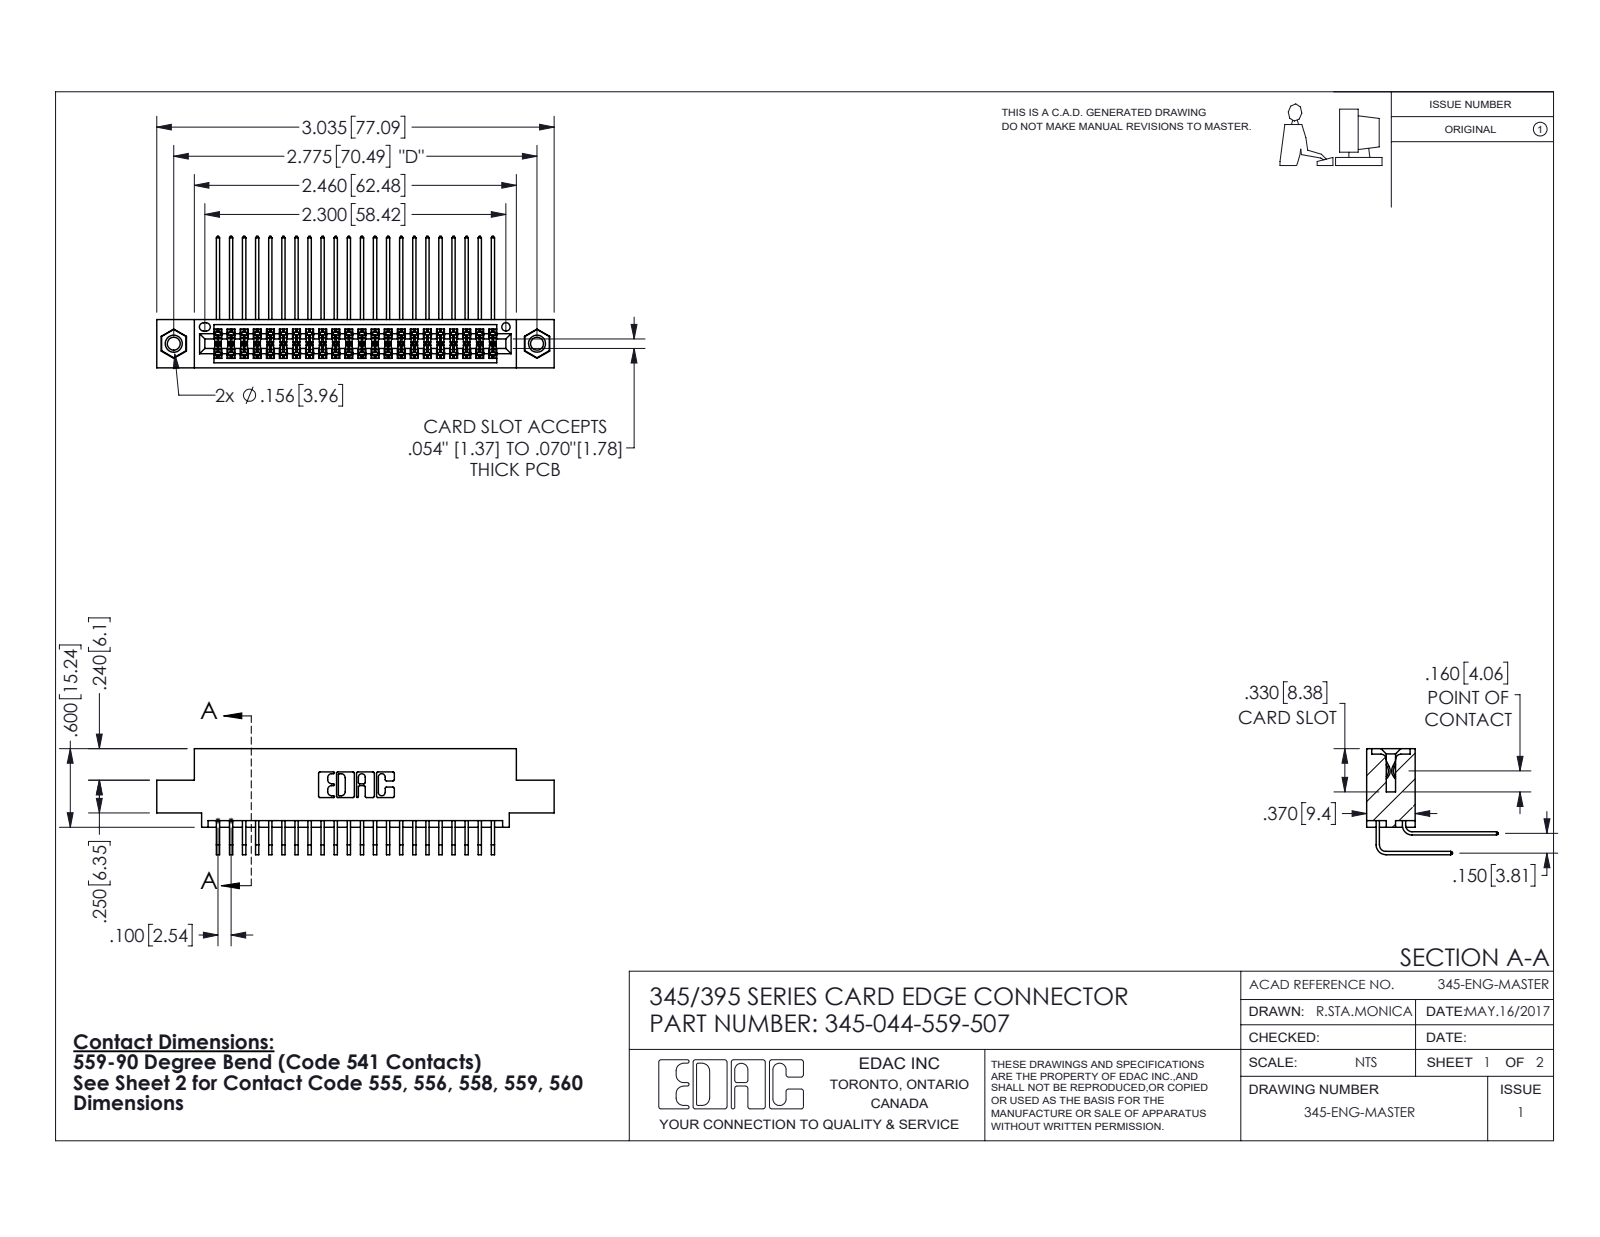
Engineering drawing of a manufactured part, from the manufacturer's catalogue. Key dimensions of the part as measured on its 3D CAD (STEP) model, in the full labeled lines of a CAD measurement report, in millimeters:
Part name (STEP PRODUCT): 345-292-001_559 Tail - 2; 345-044-559-507; 345-250-001_345-250-005-103; 345-292-001_558 559 Tail - 1 (+1 more)
STEP written by: SolidWorks 2016 (CONFIG_CONTROL_DESIGN)
Units: millimetres
Bodies: 47 solids, 2478 faces (1656 planar, 806 cylindrical, 16 other)
Overall size (bounding box): 77.1 × 25.5 × 20.5
Volume: 7 470 mm³ · Surface area: 11 970 mm²
Round holes (diameter × count): ⌀2.5 ×2, ⌀3.2 ×2, ⌀4 ×2, ⌀1.6 ×1
Round bosses / shafts (diameter × count): ⌀3.9 ×2
Partial cylindrical surfaces — rounded edges, fillets, slot ends (radius × count): R0.2 ×87, R0.3 ×22, R0.2 ×6, R0.8 ×6, R0.7 ×3, R0.4 ×2, R0.5 ×2, R0.6 ×2
Main face-to-face distances: 1.8, 7.6, 5.1, 9.4, 2.5, 6.9, 0.6, 5.7, 3.8, 4.4
Hole centre spacings: 6.9, 64.5, 70.5
